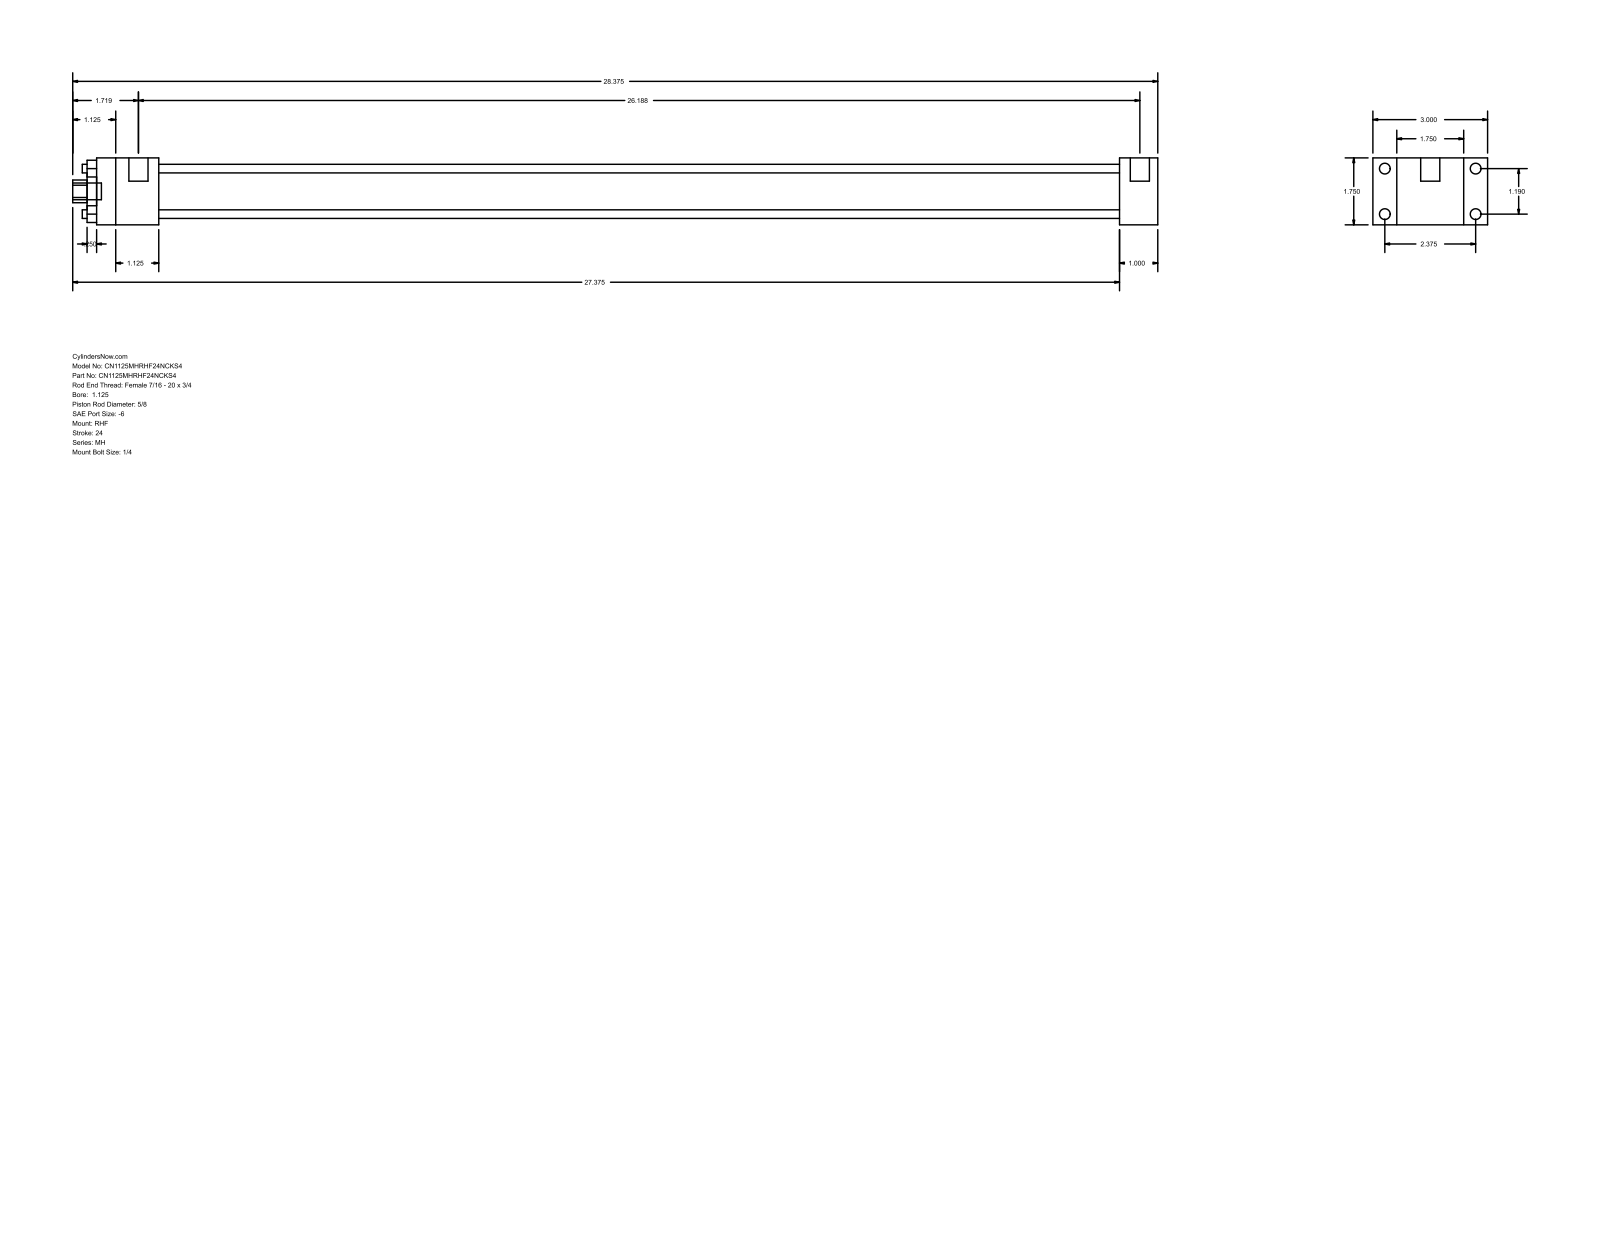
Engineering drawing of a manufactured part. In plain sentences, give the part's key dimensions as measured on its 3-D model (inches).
The part is named "MH_RHF__0112_0.625". Its 3-D file was written by "GSSL Pune (CONFIG_CONTROL_DESIGN)". It is 0 solids with 88 faces: 60 planar, 28 cylindrical and 0 other. Overall it measures 28.375 by 3 by 1.75 inches. Round holes: 4 of diameter 0.225, 1 of diameter 0.625, 1 of diameter 1.125, 1 of diameter 1.375. Round bosses or shafts: 4 of diameter 0.281, 4 of diameter 0.219, 2 of diameter 0.5, 1 of diameter 0.437. Partial cylindrical surfaces (rounded edges, fillets, slot ends): 1 of radius 0.297. The main face-to-face distances are 1.75, 0.625, 2.375, 1, 3, 25.125, 26.125, 1.625, 26.75, 27.75. The hole center spacings are 0.841, 1.19, 1.683.
